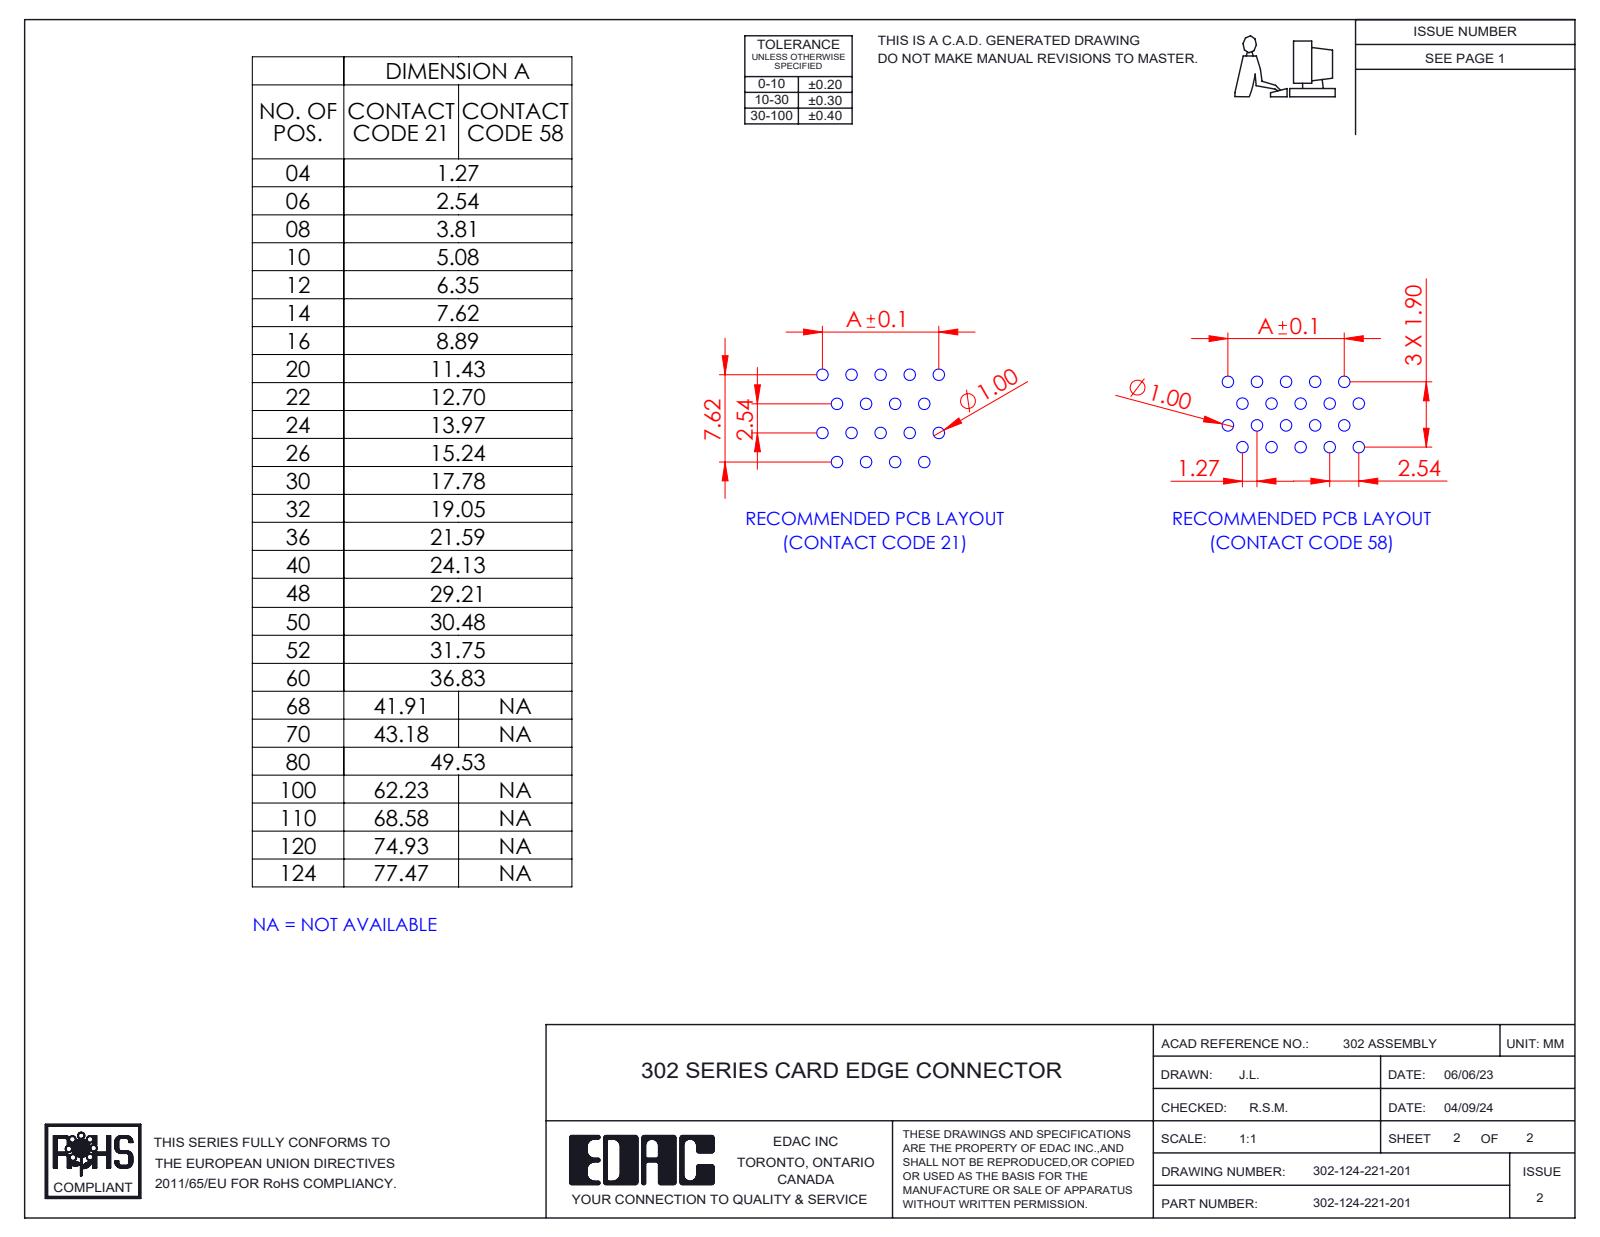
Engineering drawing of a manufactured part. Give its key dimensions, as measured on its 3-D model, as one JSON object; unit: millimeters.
{"part_name": "302-124-221-201; Contact_302-290-X21 (1); Contact_302-290-X21 (2); HSG_Vertical HSG", "step_written_by": "SolidWorks 2023 (CONFIG_CONTROL_DESIGN)", "units": "millimeters", "bodies": {"solids": 125, "faces": 5708, "planar": 4203, "cylindrical": 1253, "other": 252}, "overall_size": [84.84, 17.63, 8.88], "volume_mm3": 6440, "surface_area_mm2": 18527, "partial_cylinders_radius": [[0.2, 132], [2.03, 4], [2.09, 4], [0.11, 2], [0.4, 2], [0.41, 2], [1.25, 2], [1.53, 2]], "face_to_face_distances": [8.88, 2.54, 1.27, 5.08, 3.81, 0.8, 0.47, 3.49, 5.39, 1.9]}
